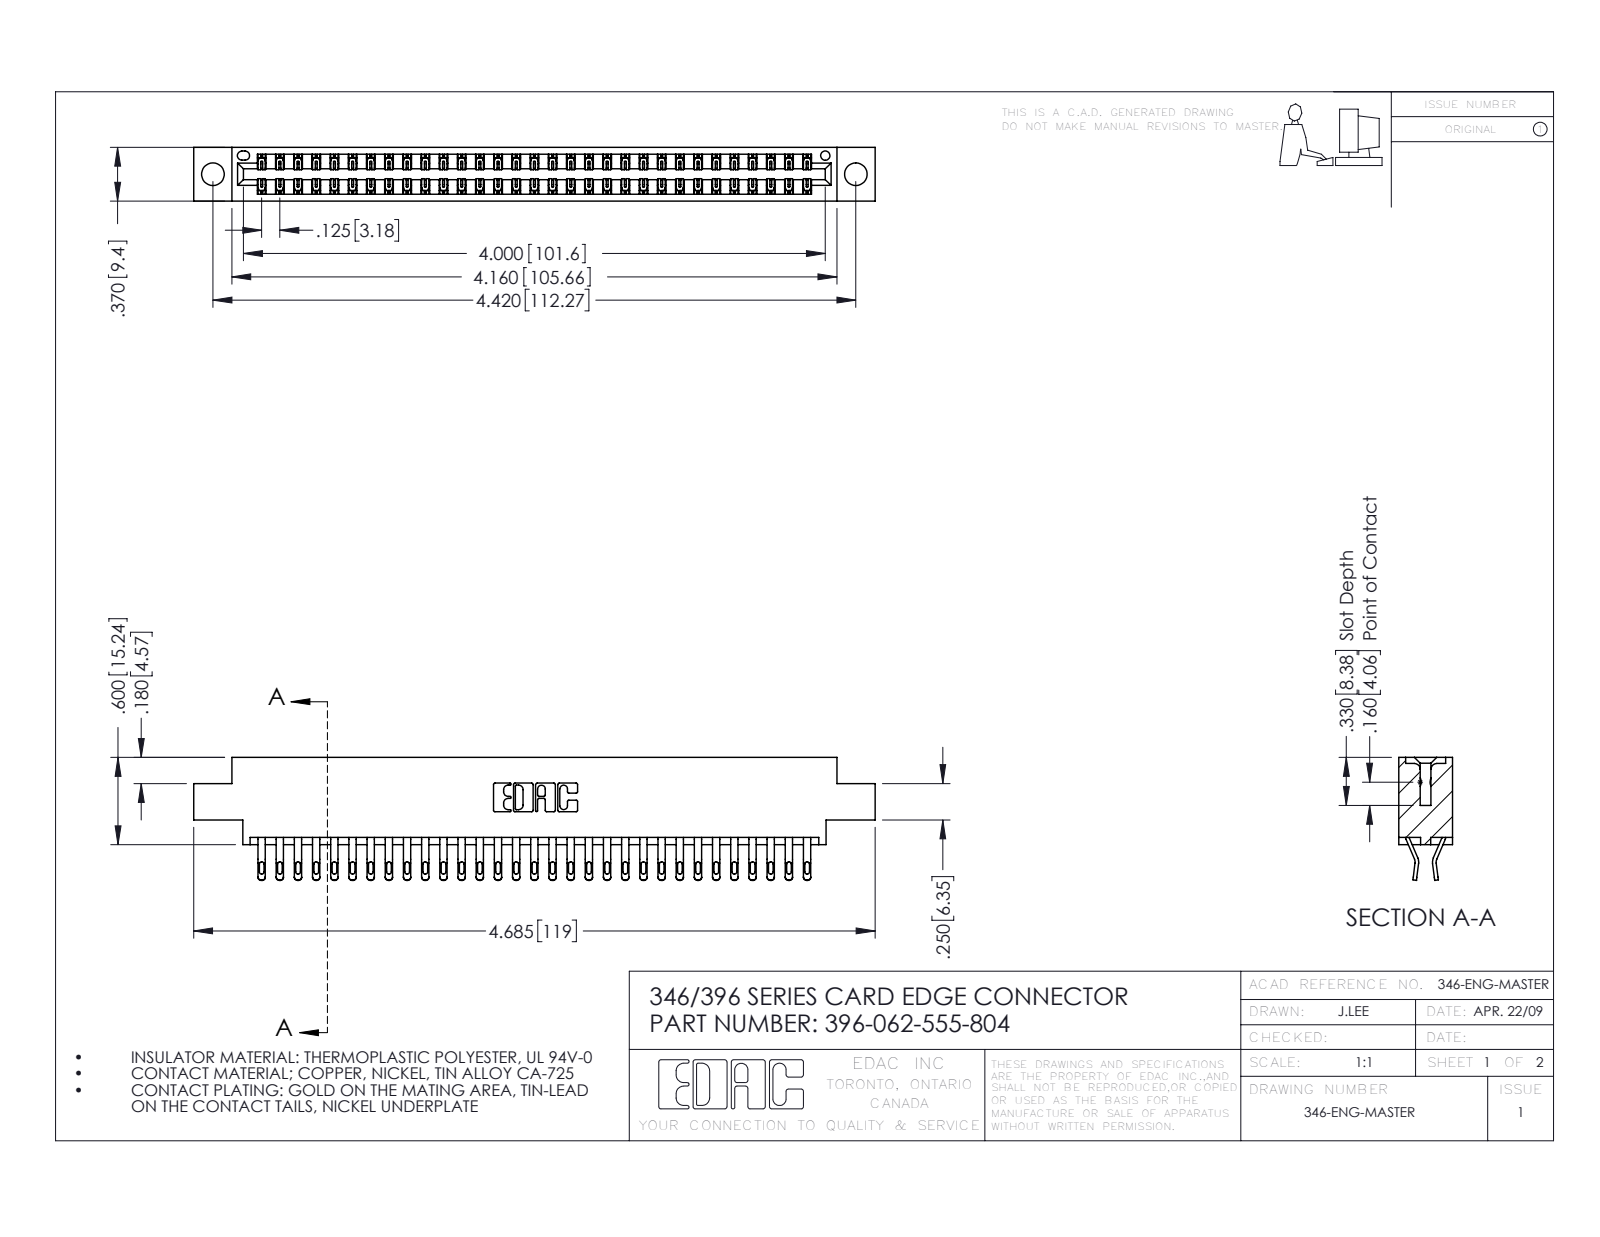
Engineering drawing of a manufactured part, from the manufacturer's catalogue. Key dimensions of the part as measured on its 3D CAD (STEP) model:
Part name (STEP PRODUCT): 346 Part_0.170 Offset - 0.156 Dia-TH; 396-062-555-804; 345-292-001_555 Tail
STEP written by: SolidWorks 2016 (CONFIG_CONTROL_DESIGN)
Units: inches
Bodies: 63 solids, 3722 faces (2126 planar, 1596 cylindrical, 0 other)
Overall size (bounding box): 4.685 × 0.845 × 0.37
Volume: 0.699 in³ · Surface area: 25.12 in²
Round holes (diameter × count): ⌀0.156 ×2, ⌀0.064 ×1
Partial cylindrical surfaces — rounded edges, fillets, slot ends (radius × count): R0.016 ×124, R0.02 ×124, R0.006 ×93, R0.01 ×22, R0.007 ×6, R0.031 ×6, R0.026 ×3, R0.01 ×2
Main face-to-face distances: 0.048, 0.322, 0.37, 0.25, 0.025, 0.072, 0.298, 0.275, 0.148, 0.222
Hole centre spacings: 0.246, 4.212, 4.42
